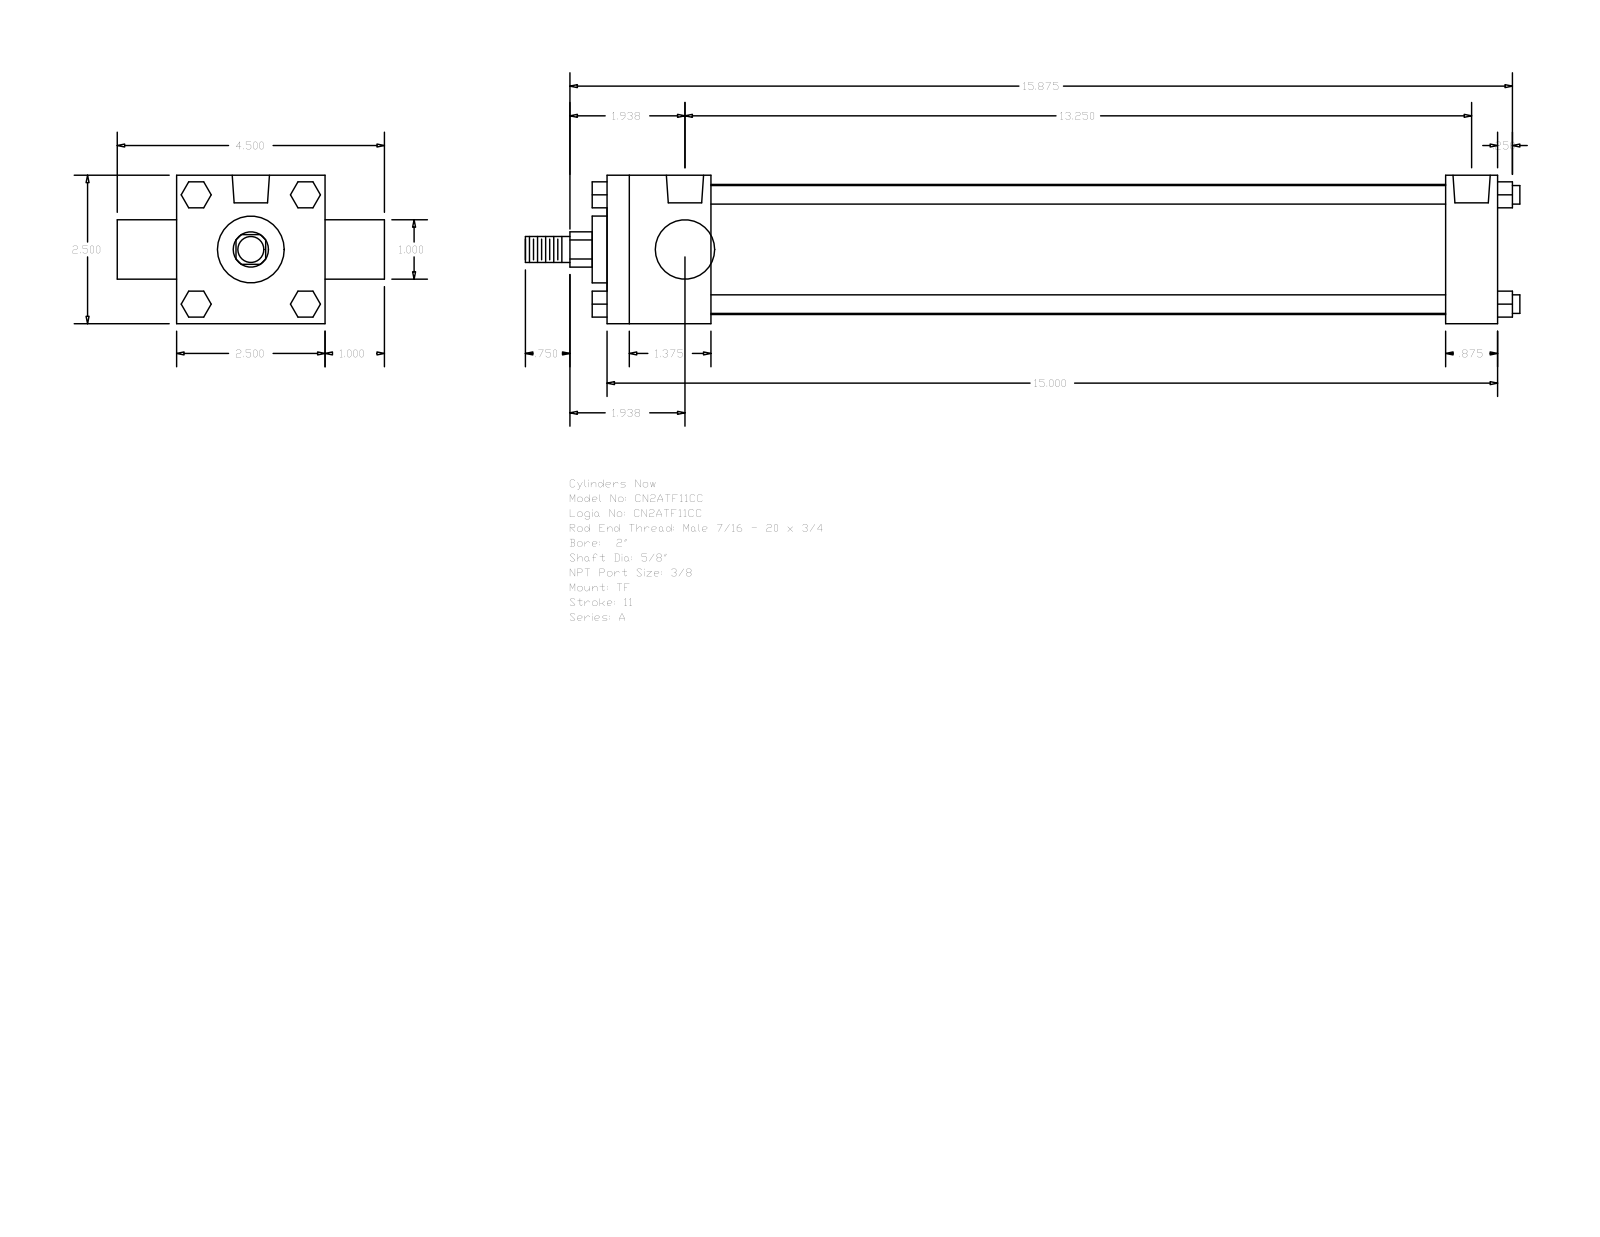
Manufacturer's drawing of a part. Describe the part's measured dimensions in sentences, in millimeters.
The part is named "A_TF__0200_0.625". Its 3-D file was written by "GSSL Pune (CONFIG_CONTROL_DESIGN)". It is 0 solids with 120 faces: 92 planar, 28 cylindrical and 0 other. Overall it measures 425.45 by 114.3 by 63.5 millimeters. Round holes: 3 of diameter 5.56, 2 of diameter 15.93. Round bosses or shafts: 4 of diameter 7.94, 1 of diameter 55.63, 1 of diameter 28.57, 1 of diameter 25.4, 1 of diameter 15.88, 1 of diameter 11.11. Partial cylindrical surfaces (rounded edges, fillets, slot ends): 1 of radius 7.54. The main face-to-face distances are 63.5, 381, 44.45, 358.77, 314.32, 336.55, 22.23, 25.4, 88.9, 6.35. The hole center spacings are 3.97, 3.98, 328.6, 332.57, 332.58, 336.55.
